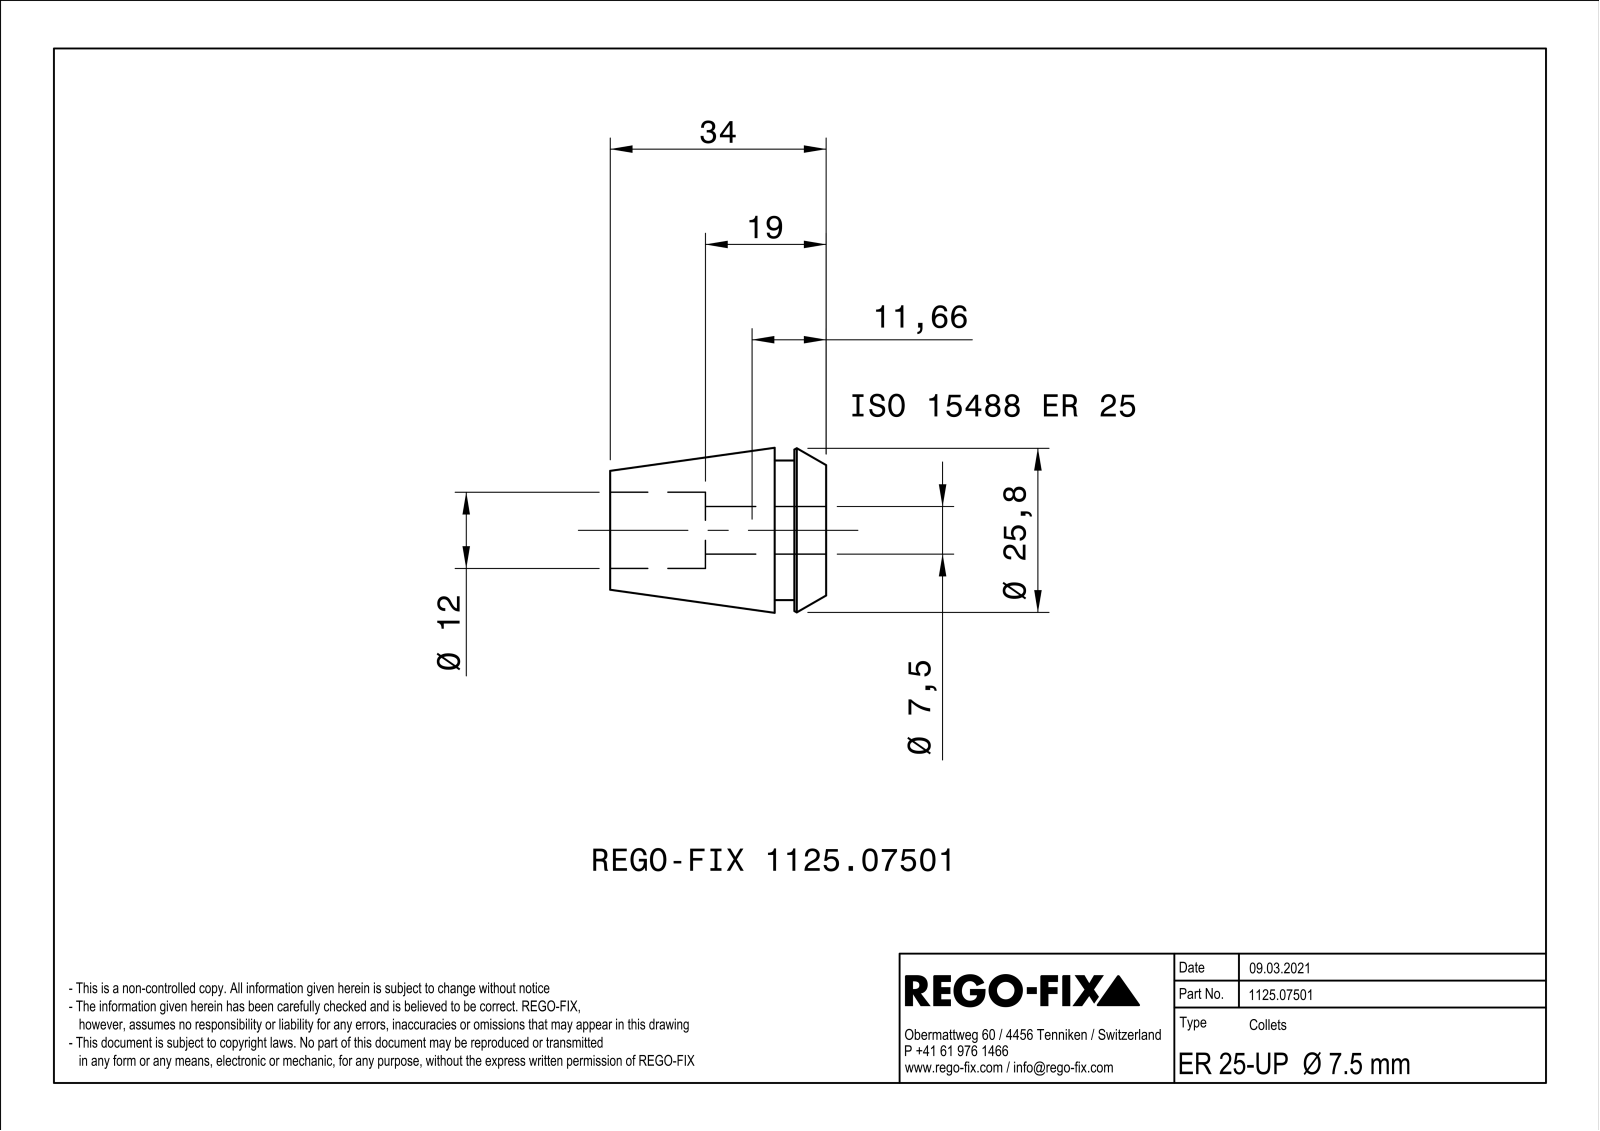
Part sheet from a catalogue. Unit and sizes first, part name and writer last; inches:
Units: inches
Overall size (bounding box): 1.339 × 1.023 × 1.023
Round holes (diameter × count): ⌀0.472 ×1
Round bosses / shafts (diameter × count): ⌀0.866 ×1
Partial cylindrical surfaces — rounded edges, fillets, slot ends (radius × count): R0.016 ×12, R0.148 ×1
Main face-to-face distances: 0.031, 0.032, 0.031, 0.319, 1.339, 1.02, 0.197, 0.122, 1.142, 0.748
Volume: 0.547 in³ · Surface area: 13.62 in²
Bodies: 1 solid, 256 faces (88 planar, 48 cylindrical, 120 other)
Part name (STEP PRODUCT): NOCUT
STEP written by: SIEMENS PLM Software Solid Edge ST10 (AUTOMOTIVE_DESIGN)
